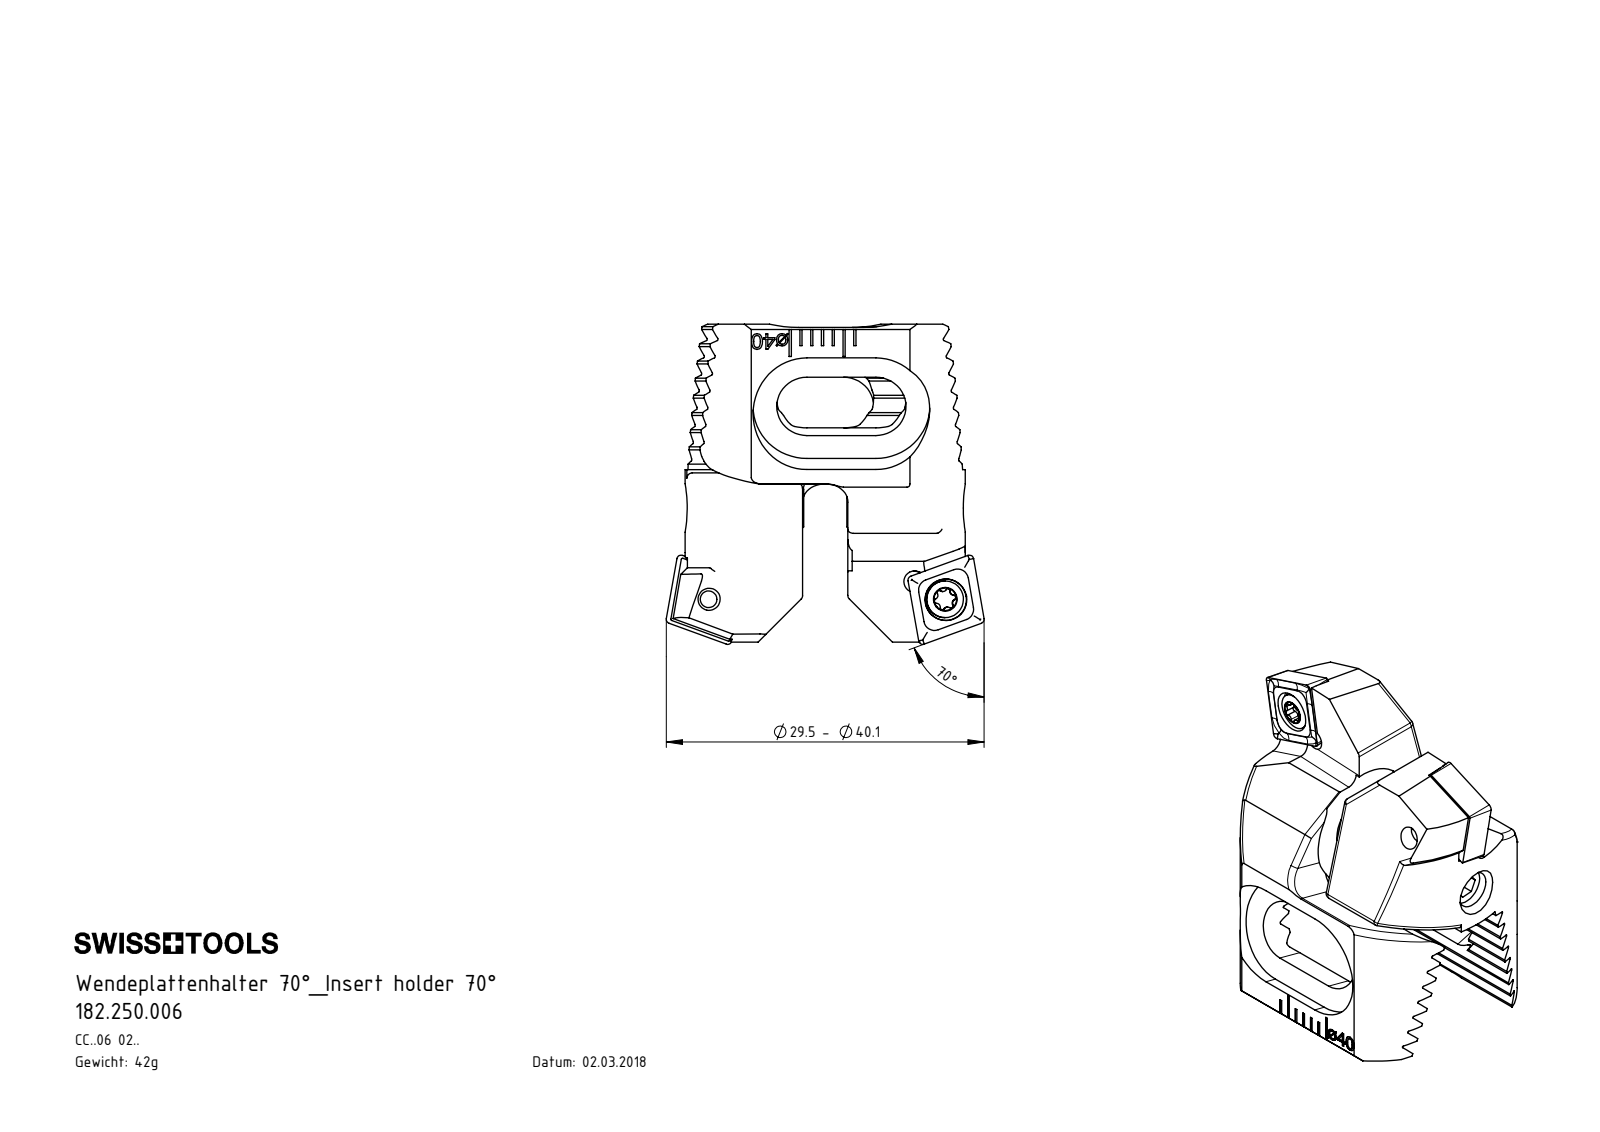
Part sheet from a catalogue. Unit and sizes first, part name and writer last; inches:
Units: inches
Overall size (bounding box): 1.169 × 1.161 × 0.799
Round holes (diameter × count): ⌀0.063 ×2, ⌀0.079 ×2, ⌀0.081 ×2, ⌀0.11 ×2, ⌀0.152 ×2, ⌀0.138 ×1
Round bosses / shafts (diameter × count): ⌀0.134 ×2, ⌀0.098 ×2, ⌀0.157 ×1
Partial cylindrical surfaces — rounded edges, fillets, slot ends (radius × count): R0.005 ×16, R0.02 ×16, R0.008 ×12, R0.014 ×10, R0.039 ×4, R0.079 ×4, R0.11 ×4, R0.197 ×4
Main face-to-face distances: 0.056, 0.113, 0.169, 0.225, 0.281, 0.154, 0.181, 0.338, 0.394, 0.016
Hole centre spacings: 0.129, 0.132, 0.276, 0.767, 0.77, 0.878, 0.532, 0.652
Volume: 0.318 in³ · Surface area: 7.401 in²
Bodies: 8 solids, 634 faces (316 planar, 142 cylindrical, 176 other)
Part name (STEP PRODUCT): Z25-xxx.001.016_B_70ø; CCMT060204; Z25-ER3.001.010_A; WCA-ER2.001.006_A (+1 more)
STEP written by: SolidWorks 2017 (CONFIG_CONTROL_DESIGN)
